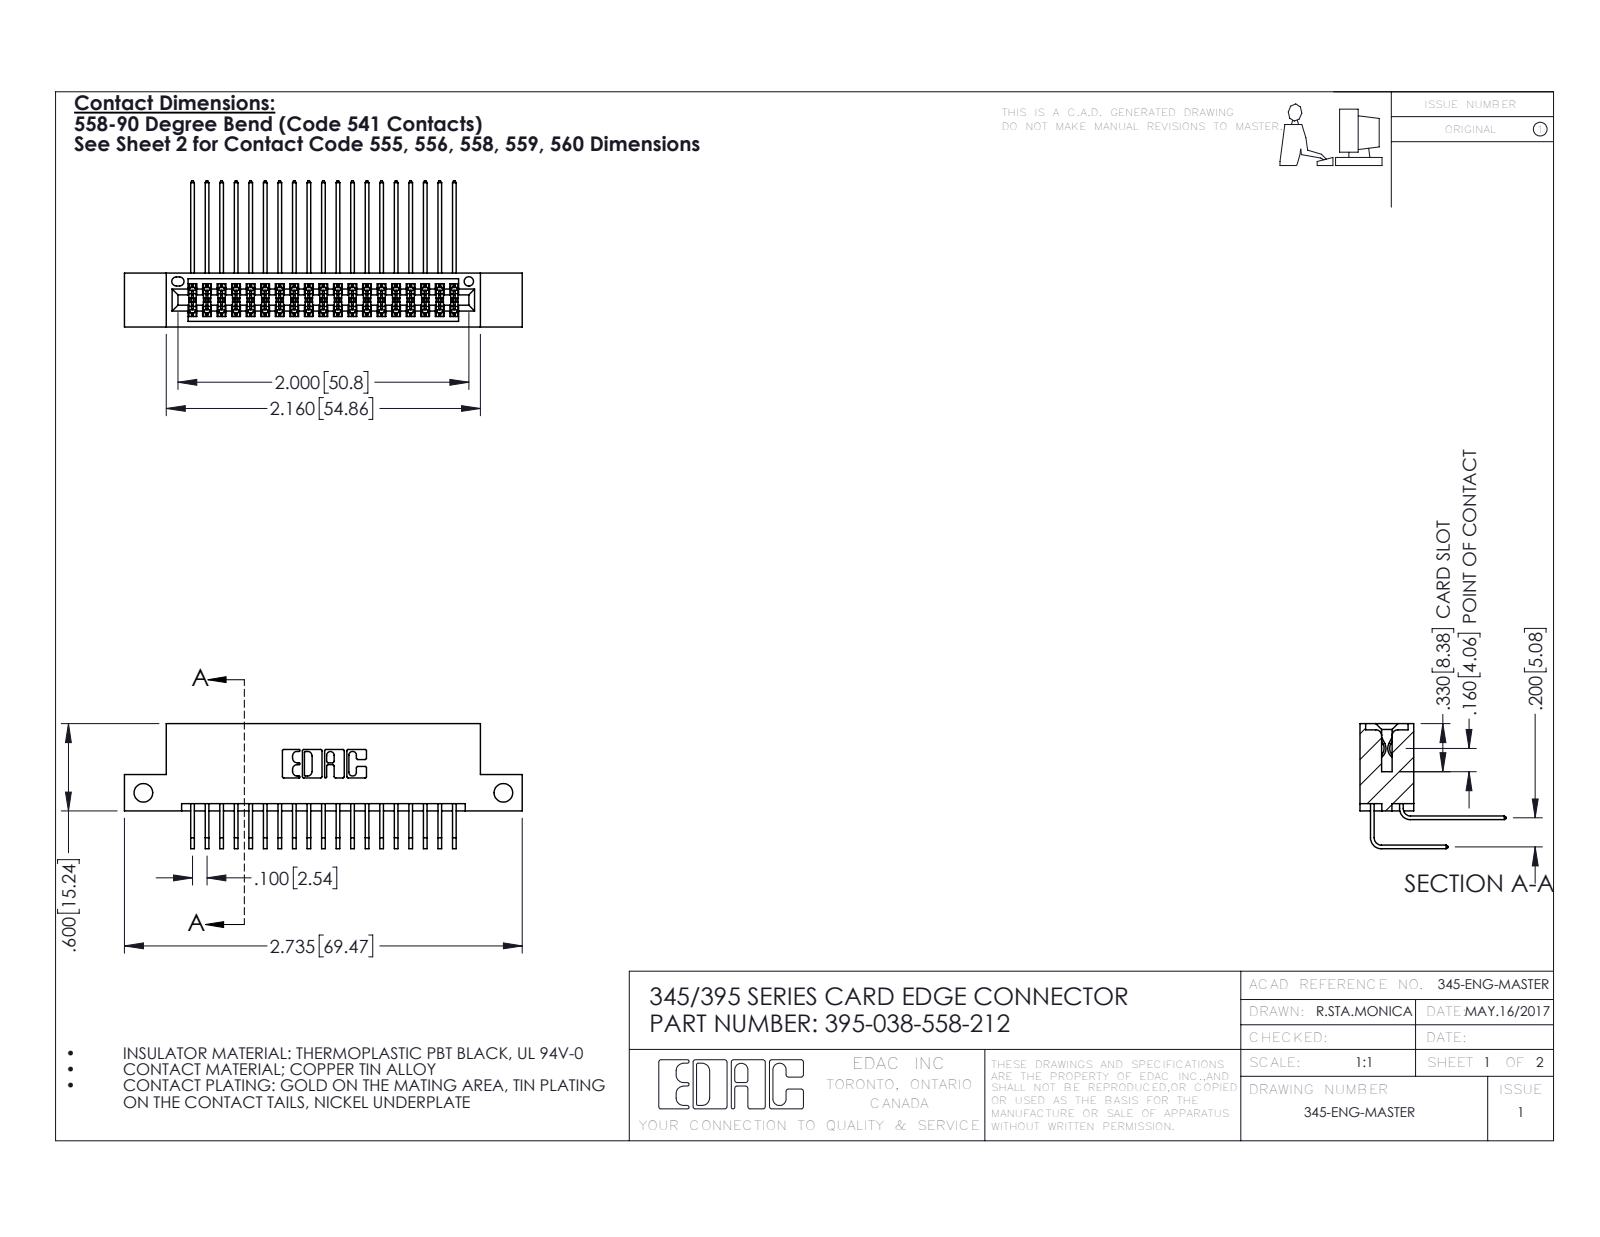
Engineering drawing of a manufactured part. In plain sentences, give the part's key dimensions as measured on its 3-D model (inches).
The part is named "345 Part_Flush Mounting Lugs - Side Mount; 345-292-001_558 559 Tail - 1; 395-038-558-212; 345-292-001_558 Tail - 2". Its 3-D file was written by "SolidWorks 2016 (CONFIG_CONTROL_DESIGN)". It is 39 solids with 2102 faces: 1410 planar, 692 cylindrical and 0 other. Overall it measures 2.735 by 1.005 by 0.859 inches. Its volume is 0.407 cubic inches and its surface area 15.97 square inches. Round holes: 2 of diameter 0.128, 1 of diameter 0.064. Partial cylindrical surfaces (rounded edges, fillets, slot ends): 58 of radius 0.006, 22 of radius 0.01, 6 of radius 0.007, 6 of radius 0.031, 3 of radius 0.026, 2 of radius 0.014, 2 of radius 0.019, 2 of radius 0.022. The main face-to-face distances are 0.2, 0.072, 0.298, 0.37, 0.098, 0.272, 0.025, 0.225, 0.285, 0.025. The hole center spacings are 2.475.
